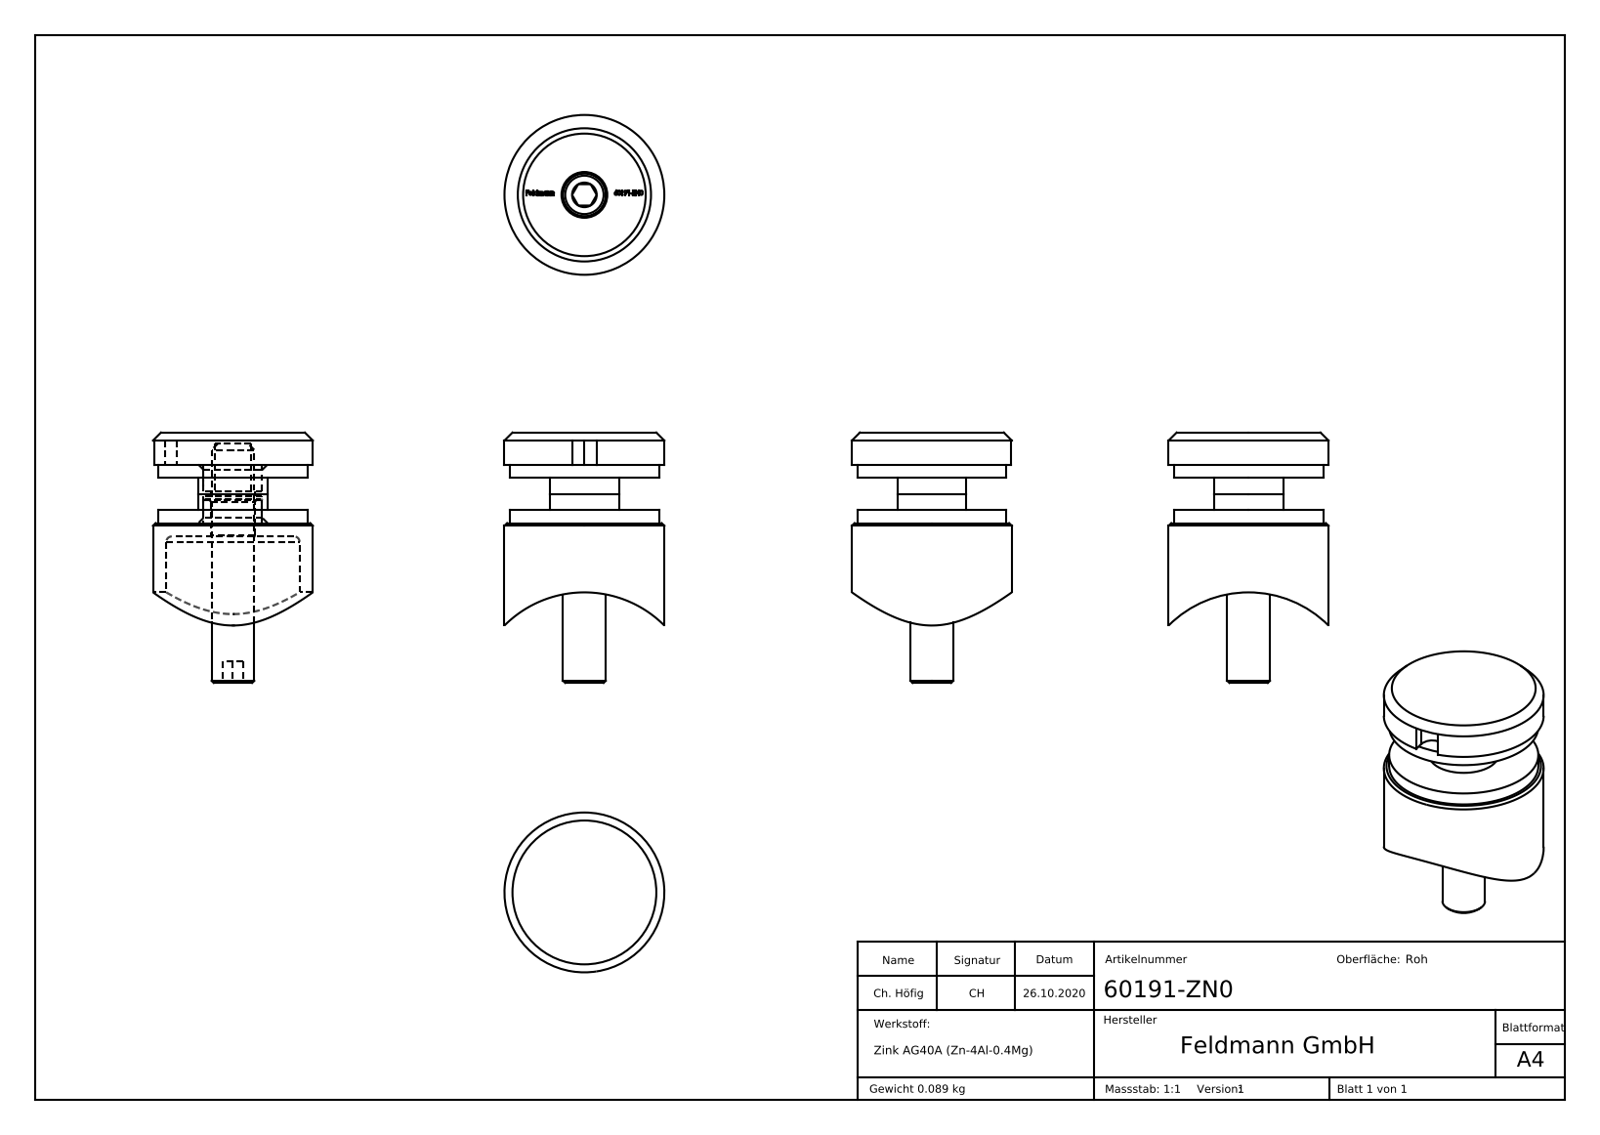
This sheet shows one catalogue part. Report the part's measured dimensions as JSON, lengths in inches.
{"part_name": "6019X-240 Teil3; DIN913 M8x45_DIN913 M8x45; DIN913 M8x45; 60190-240 Teil2_60191-ZN0 Teil2 (+5 more)", "step_written_by": "SolidWorks 2018 (CONFIG_CONTROL_DESIGN)", "units": "inches", "bodies": {"solids": 5, "faces": 290, "planar": 145, "cylindrical": 35, "other": 110}, "overall_size": [1.85, 1.181, 1.181], "volume_in3": 0.839, "surface_area_in2": 16.87, "round_holes": [[0.268, 1], [0.323, 1], [0.433, 1], [0.984, 1]], "round_bosses_or_shafts": [[1.181, 1], [1.102, 1], [0.512, 1], [0.315, 1]], "partial_cylinders_radius": [[0.089, 1], [0.835, 1]], "face_to_face_distances": [0.433, 0.094, 0.339, 0.236, 0.669, 0.331, 0.244, 0.575, 0.098, 0.193]}
